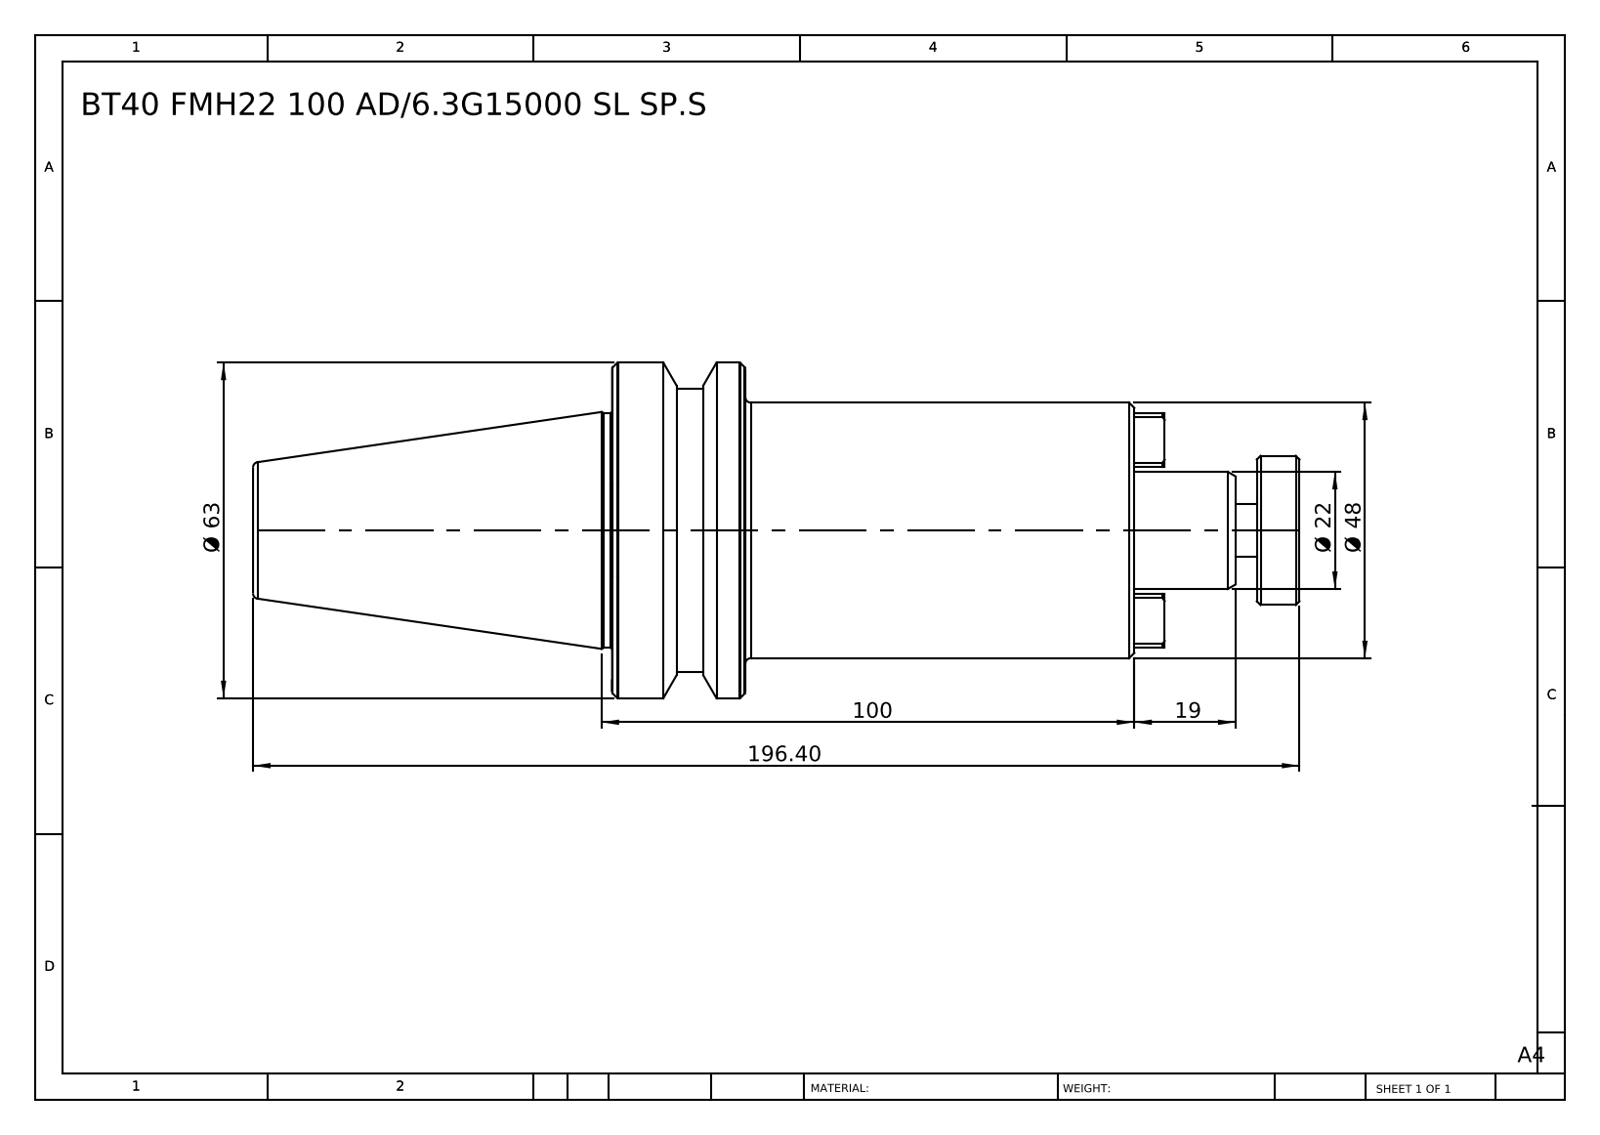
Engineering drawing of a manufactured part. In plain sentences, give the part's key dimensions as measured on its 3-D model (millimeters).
The part is named "BT40 FMH22 100 AD-6.3G15000 SL SP.S". Its 3-D file was written by "SolidWorks 2014 (CONFIG_CONTROL_DESIGN)". It is 1 solid with 91 faces: 35 planar, 16 cylindrical and 40 other. Overall it measures 196.4 by 63 by 63 millimeters. Its volume is 283 930 cubic millimeters and its surface area 32 713 square millimeters. Round bosses or shafts: 1 of diameter 63, 1 of diameter 53, 1 of diameter 48, 1 of diameter 44, 1 of diameter 28, 1 of diameter 22, 1 of diameter 10. The main face-to-face distances are 98, 73, 25, 31, 104, 129, 8, 23, 96, 121.
